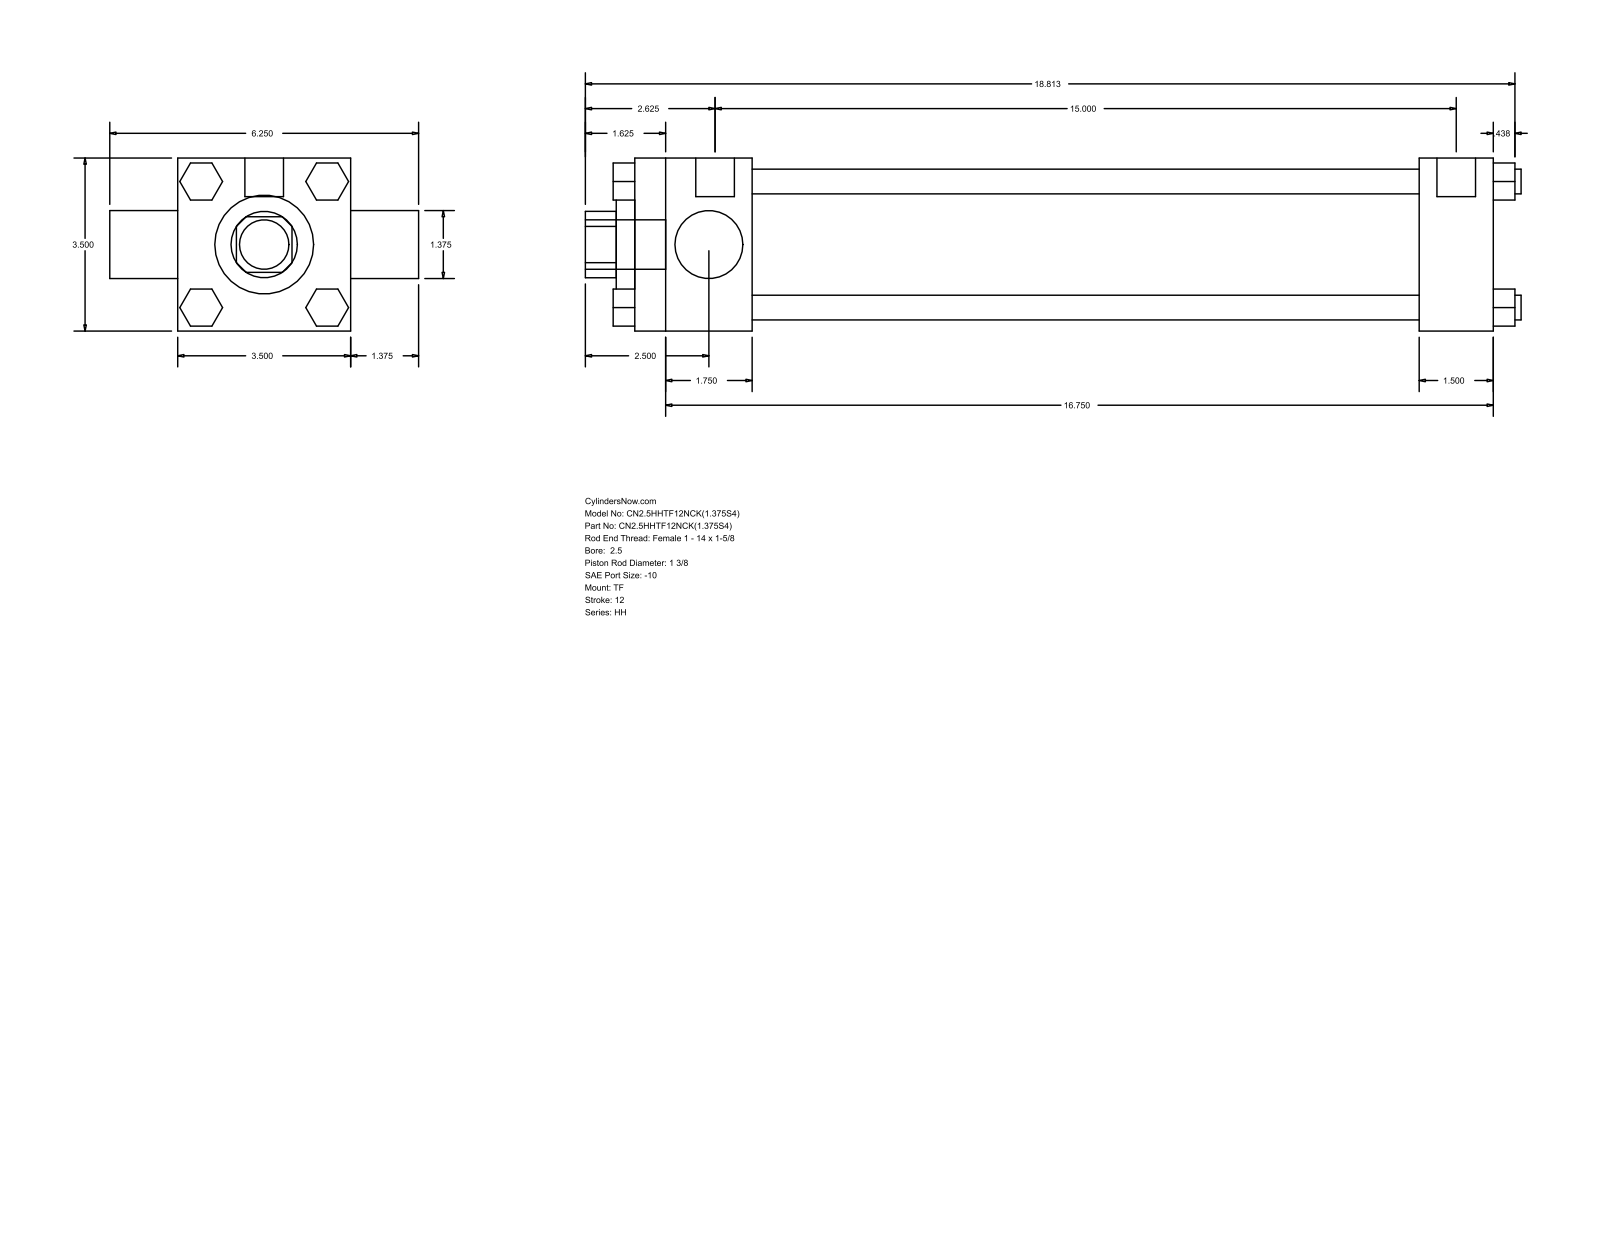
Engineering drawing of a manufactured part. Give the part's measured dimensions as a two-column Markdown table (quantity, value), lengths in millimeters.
| quantity | value |
| --- | --- |
| part name | HH_TF__0250_1.375 |
| STEP written by | GSSL Pune (CONFIG_CONTROL_DESIGN) |
| units | millimeters |
| bodies | 0 solids, 120 faces (92 planar, 28 cylindrical, 0 other) |
| overall size | 481.01 × 158.75 × 88.9 |
| round holes (diameter × count) | 34.92 × 2, 50.8 × 1, 73.03 × 1 |
| round bosses / shafts (diameter × count) | 12.7 × 4, 5.56 × 3, 19.84 × 2, 25.4 × 1 |
| partial cylindrical surfaces (radius × count) | 17.06 × 1 |
| main face-to-face distances | 88.9, 441.33, 60.32, 381.01, 403.22, 342.9, 38.11, 19.05, 32.38, 56.09 |
